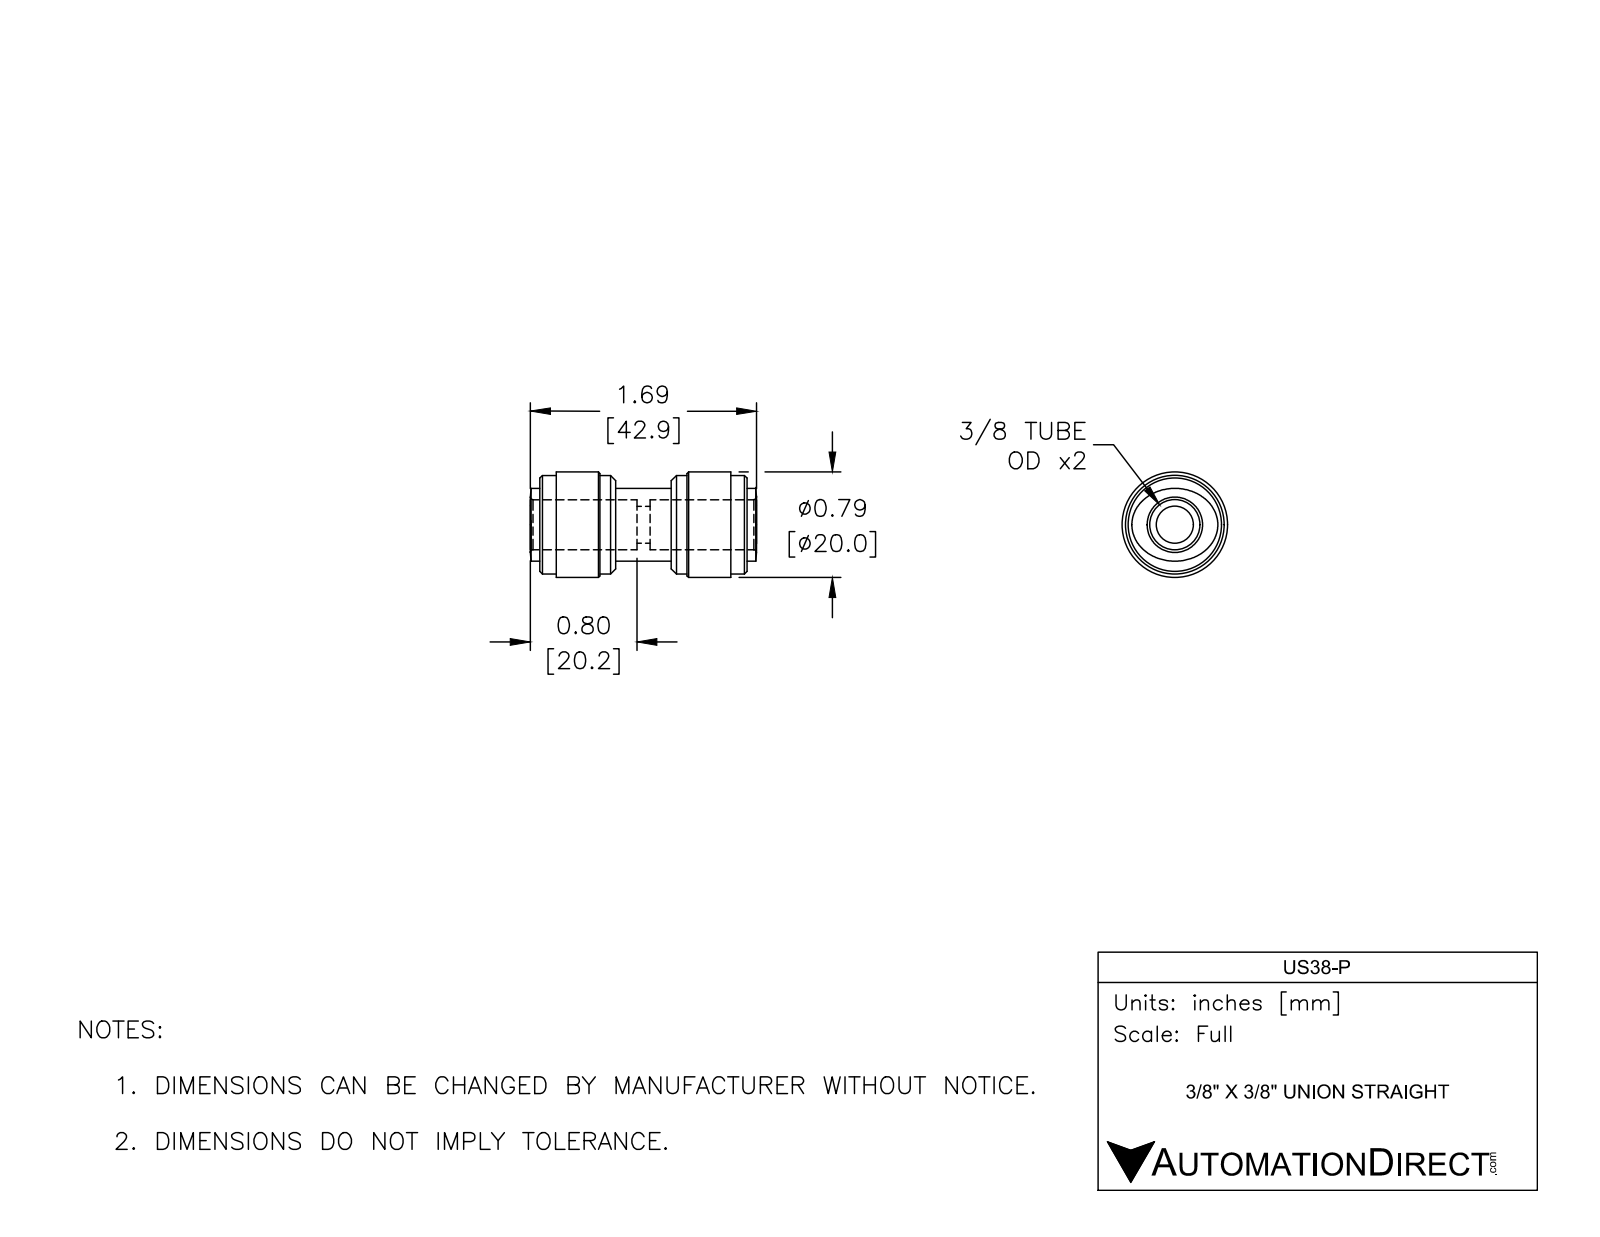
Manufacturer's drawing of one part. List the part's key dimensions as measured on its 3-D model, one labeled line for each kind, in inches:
Part name (STEP PRODUCT): US38-P
STEP written by: SolidWorks 2017 (AUTOMOTIVE_DESIGN)
Units: inches
Bodies: 1 solid, 54 faces (10 planar, 20 cylindrical, 24 other)
Overall size (bounding box): 1.689 × 0.787 × 0.787
Volume: 0.471 in³ · Surface area: 6.774 in²
Round holes (diameter × count): ⌀0.276 ×1, ⌀0.374 ×1
Round bosses / shafts (diameter × count): ⌀0.787 ×1, ⌀0.736 ×1, ⌀0.543 ×1
Main face-to-face distances: 0.567, 0.98, 0.122, 1.425, 0.445, 0.858, 0.413, 1.547, 0.724, 0.823
